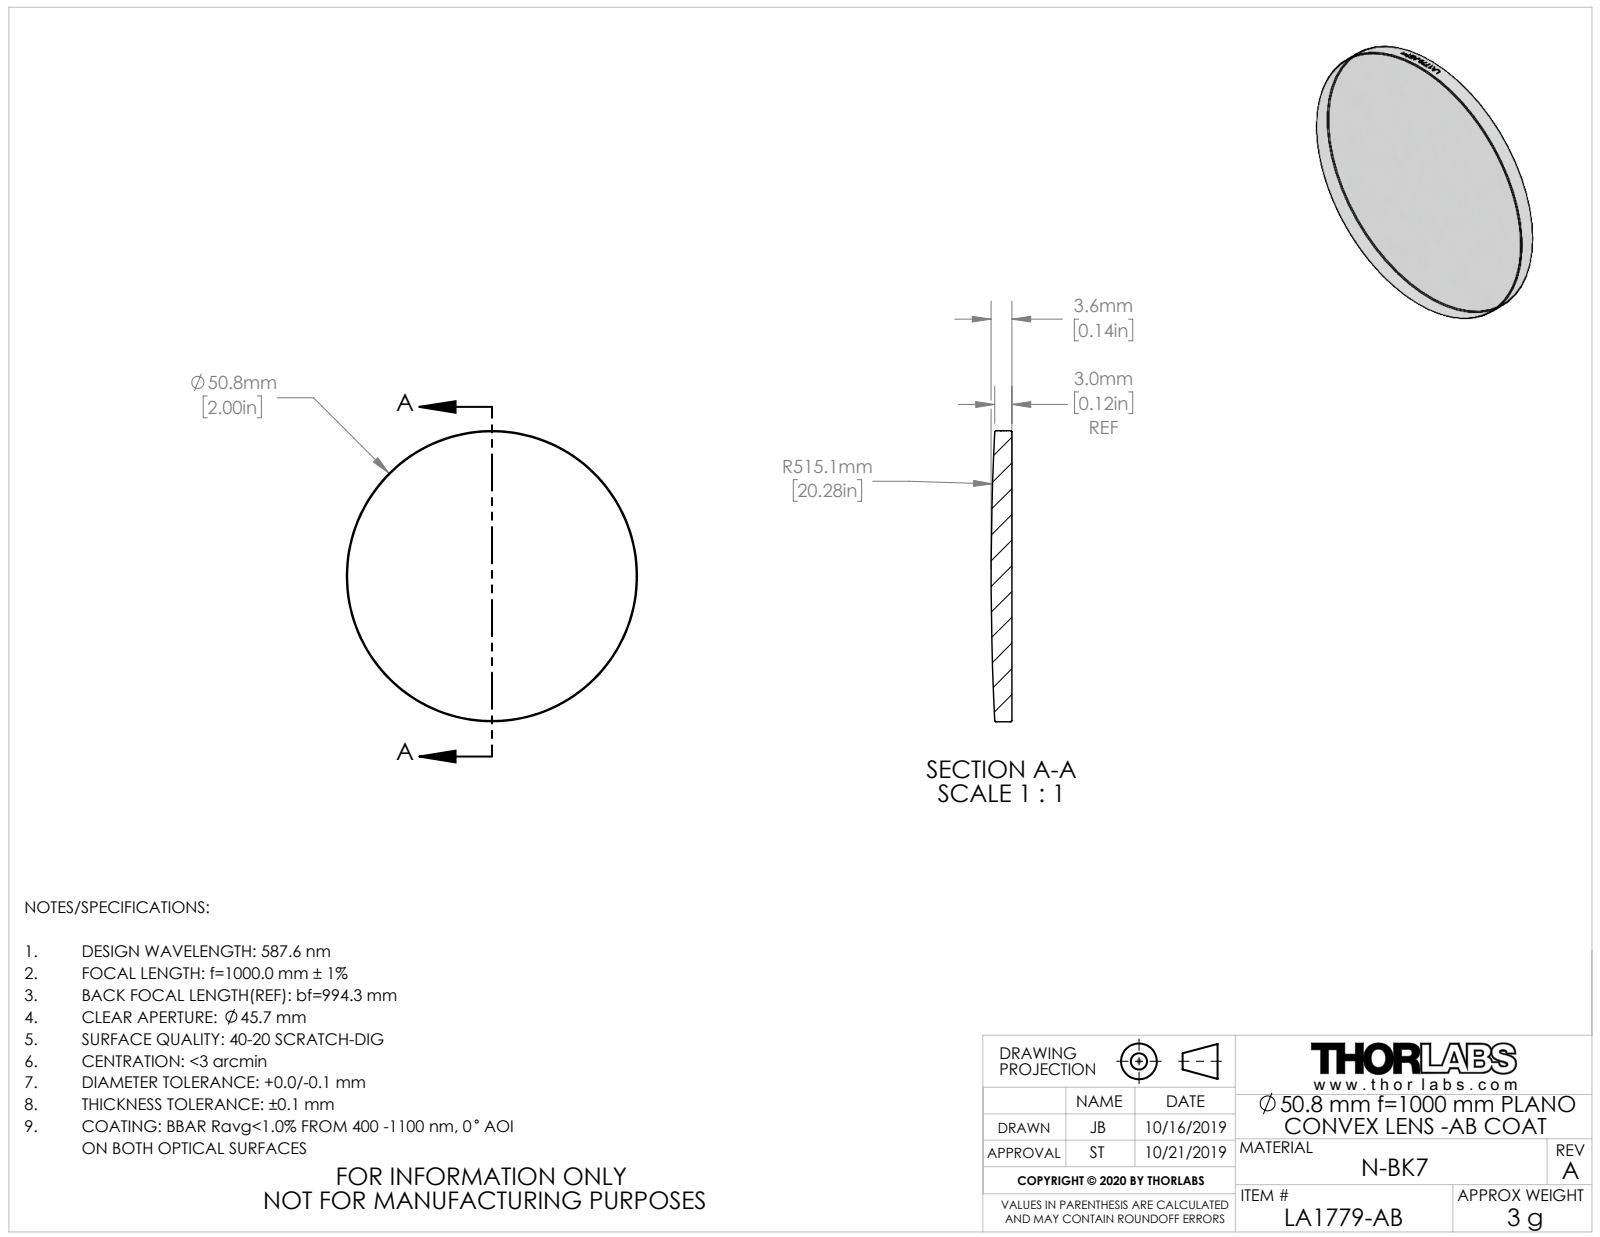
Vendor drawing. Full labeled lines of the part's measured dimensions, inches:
Part name (STEP PRODUCT): TTN195809-E0W
STEP written by: SolidWorks 2018 (CONFIG_CONTROL_DESIGN)
Units: inches
Bodies: 1 solid, 27 faces (1 planar, 20 cylindrical, 6 other)
Overall size (bounding box): 2 × 2 × 0.143
Volume: 0.409 in³ · Surface area: 6.977 in²
Round bosses / shafts (diameter × count): ⌀2 ×1
